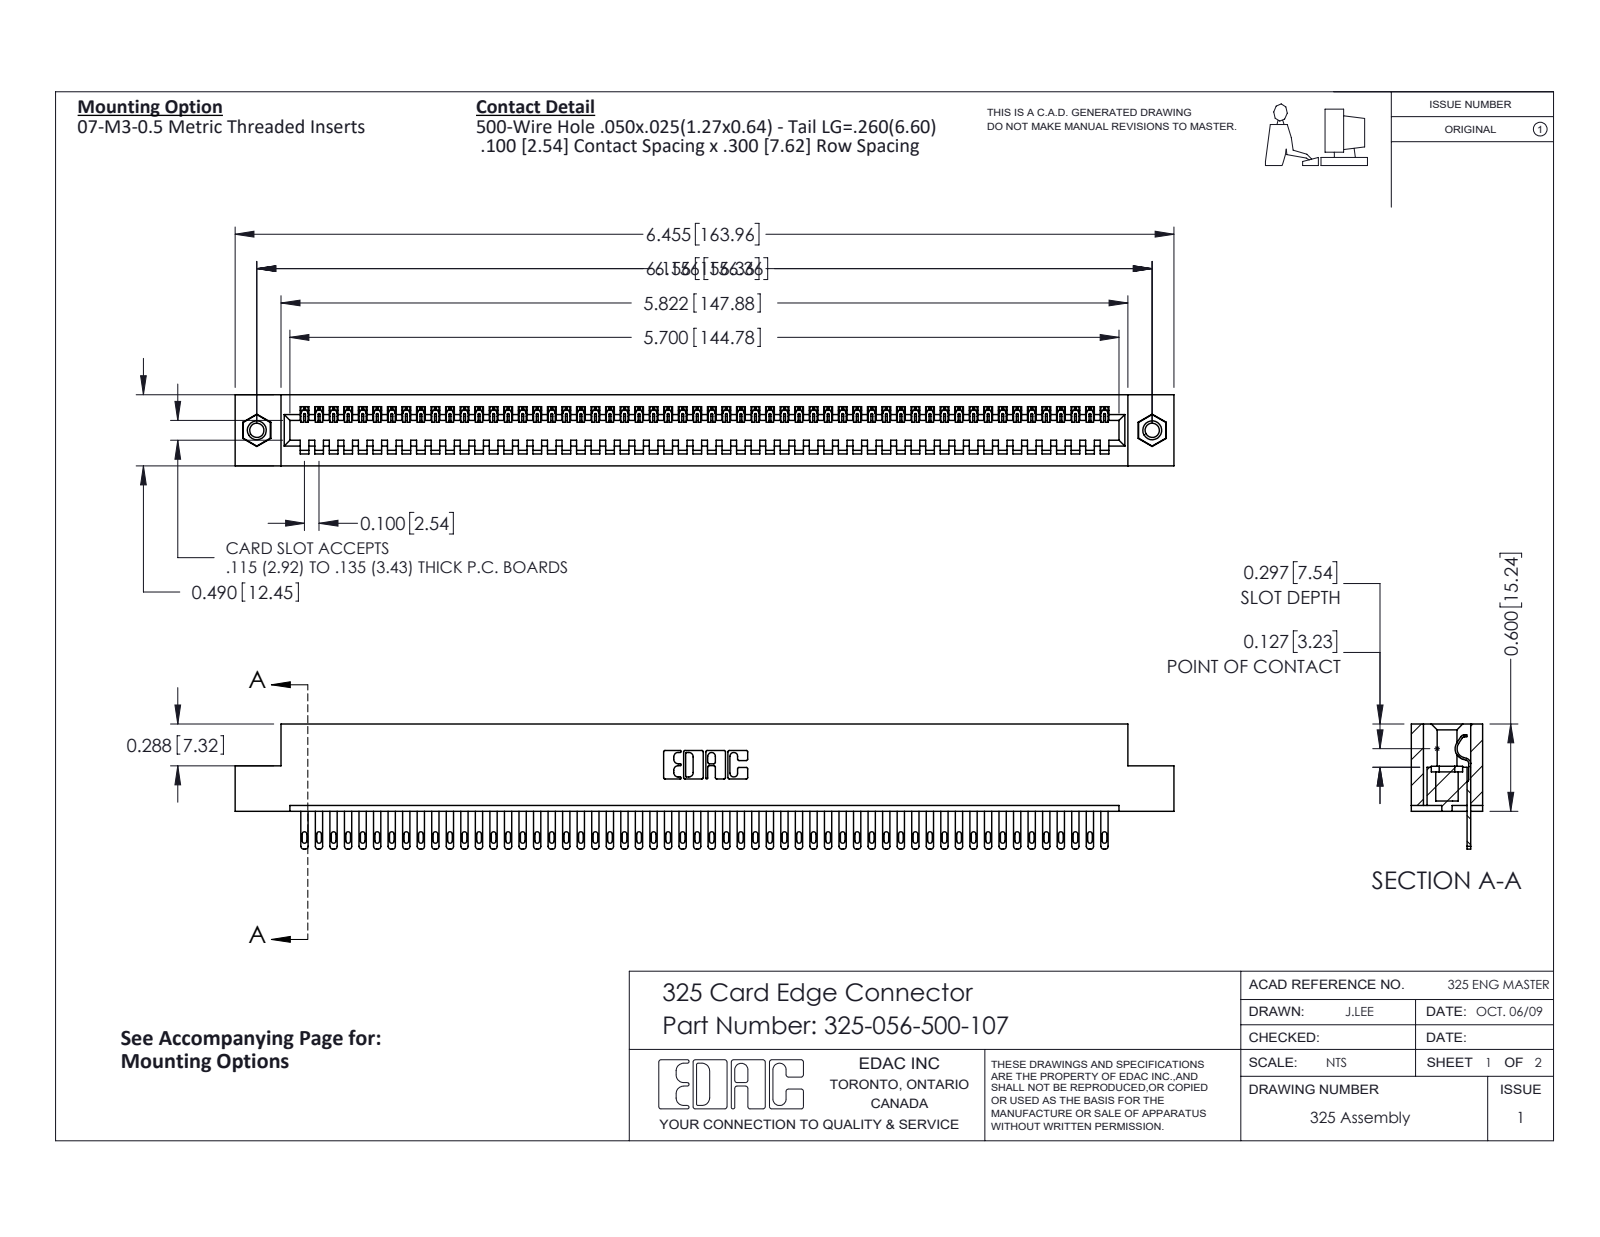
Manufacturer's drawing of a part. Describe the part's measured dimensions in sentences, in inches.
The part is named "325-056-500-107; 325-292-001_325-293-100; 325 Part_TI; 345-250-001_345-250-005-103". Its 3-D file was written by "SolidWorks 2016 (CONFIG_CONTROL_DESIGN)". It is 59 solids with 3198 faces: 2118 planar, 1064 cylindrical and 16 other. Overall it measures 6.455 by 0.86 by 0.49 inches. Its volume is 1.278 cubic inches and its surface area 36.08 square inches. Round holes: 2 of diameter 0.098, 2 of diameter 0.125, 2 of diameter 0.16. Round bosses or shafts: 2 of diameter 0.155. Partial cylindrical surfaces (rounded edges, fillets, slot ends): 112 of radius 0.006, 112 of radius 0.016, 112 of radius 0.02, 22 of radius 0.01, 6 of radius 0.007, 6 of radius 0.031, 3 of radius 0.026, 1 of radius 0.014. The main face-to-face distances are 0.083, 0.407, 0.49, 0.107, 0.383, 0.025, 0.3, 0.325, 0.263, 0.56. The hole center spacings are 6.156.
